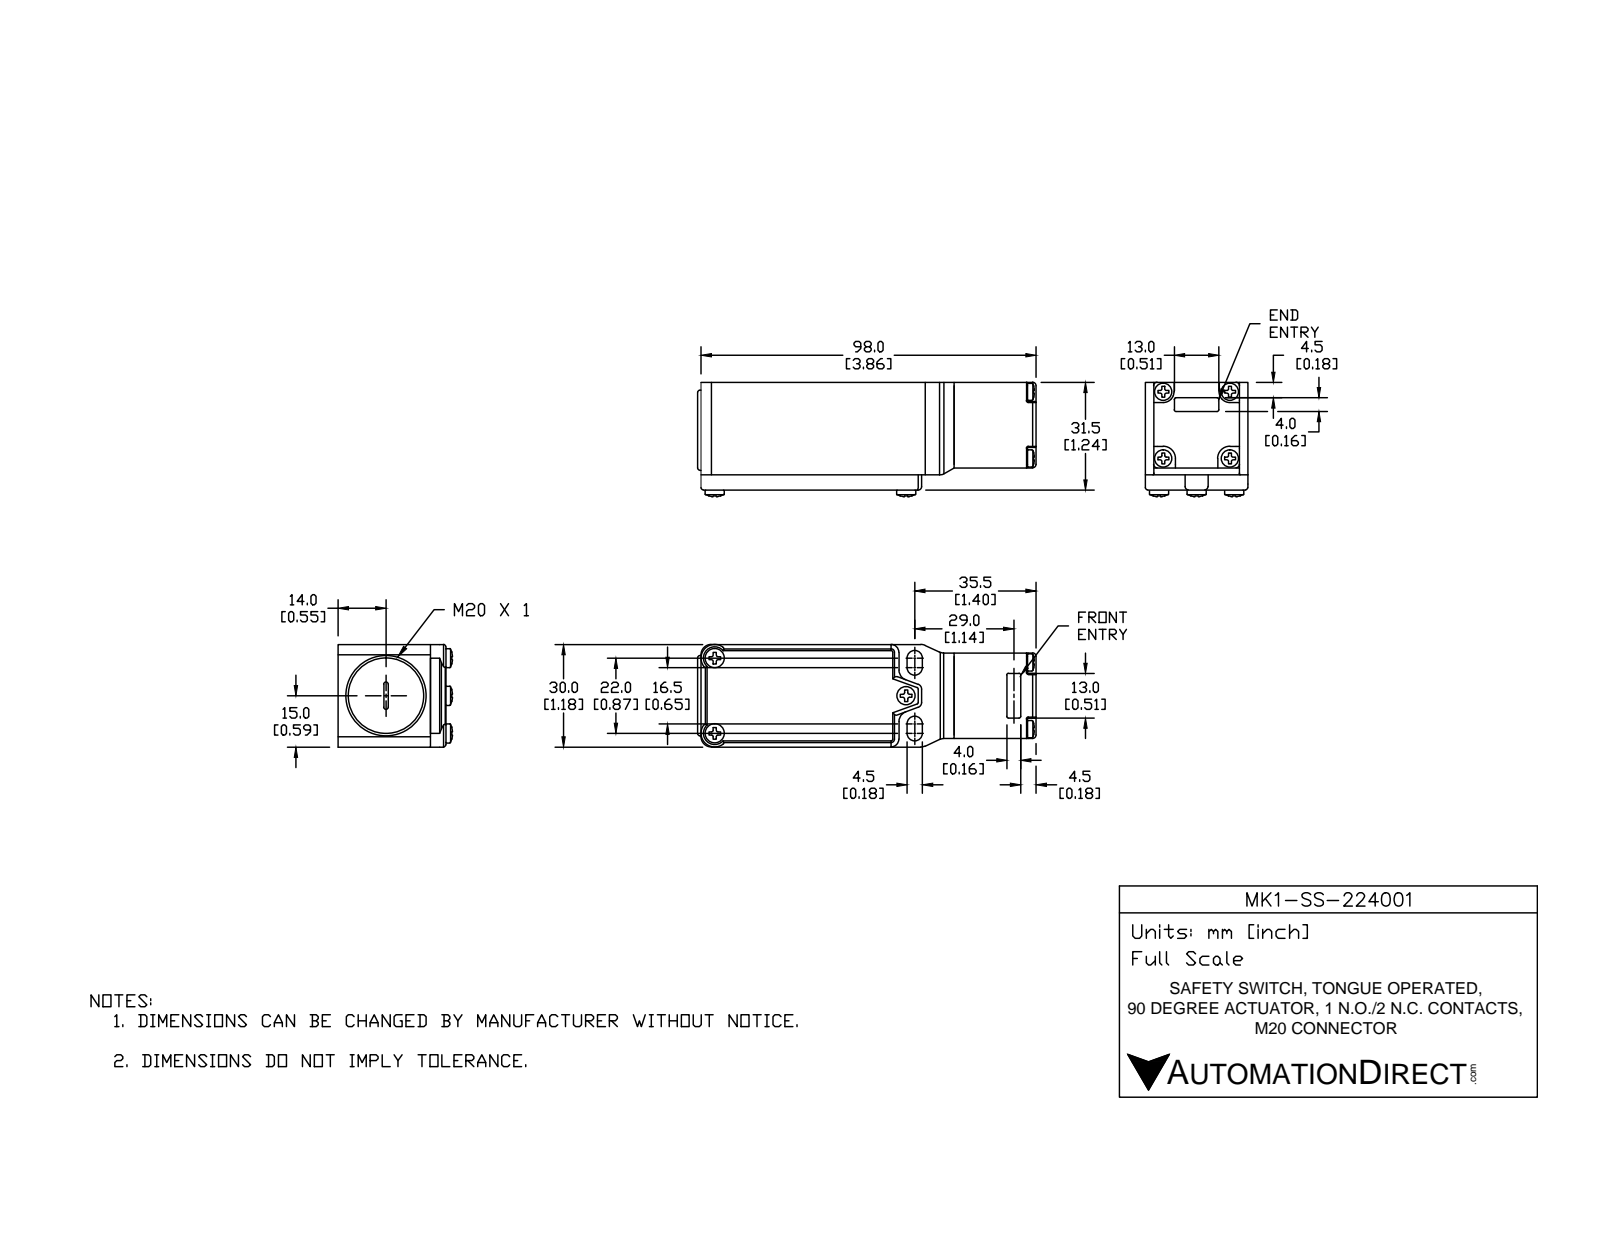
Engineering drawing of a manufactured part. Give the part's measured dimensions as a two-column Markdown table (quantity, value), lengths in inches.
| quantity | value |
| --- | --- |
| part name | MK1-SS-224001 |
| STEP written by | SolidWorks 2014 (AUTOMOTIVE_DESIGN) |
| units | inches |
| bodies | 12 solids, 1178 faces (346 planar, 474 cylindrical, 358 other) |
| overall size | 3.898 × 1.317 × 1.181 |
| volume | 2.278 in³ |
| surface area | 48.69 in² |
| round holes (diameter × count) | 0.098 × 8, 0.126 × 7, 0.157 × 3, 0.059 × 2, 0.071 × 2, 0.087 × 2, 0.142 × 2, 0.114 × 1, 0.173 × 1, 0.217 × 1, 0.406 × 1, 0.535 × 1 |
| round bosses / shafts (diameter × count) | 0.118 × 7, 0.197 × 5, 0.138 × 4, 0.22 × 3, 0.925 × 1, 0.697 × 1, 0.236 × 1 |
| partial cylindrical surfaces (radius × count) | 0.02 × 159, 0.012 × 58, 0.039 × 24, 0.006 × 14, 0.028 × 8, 0.031 × 8, 0.118 × 8, 0.089 × 4 |
| main face-to-face distances | 0.098, 0.079, 1.142, 0.114, 1.067, 1.181, 1.24, 0.177, 0.039, 0.969 |
| hole center spacings | 0.543, 0.768, 0.187, 0.423, 0.426, 0.476, 0.503, 0.581 |
